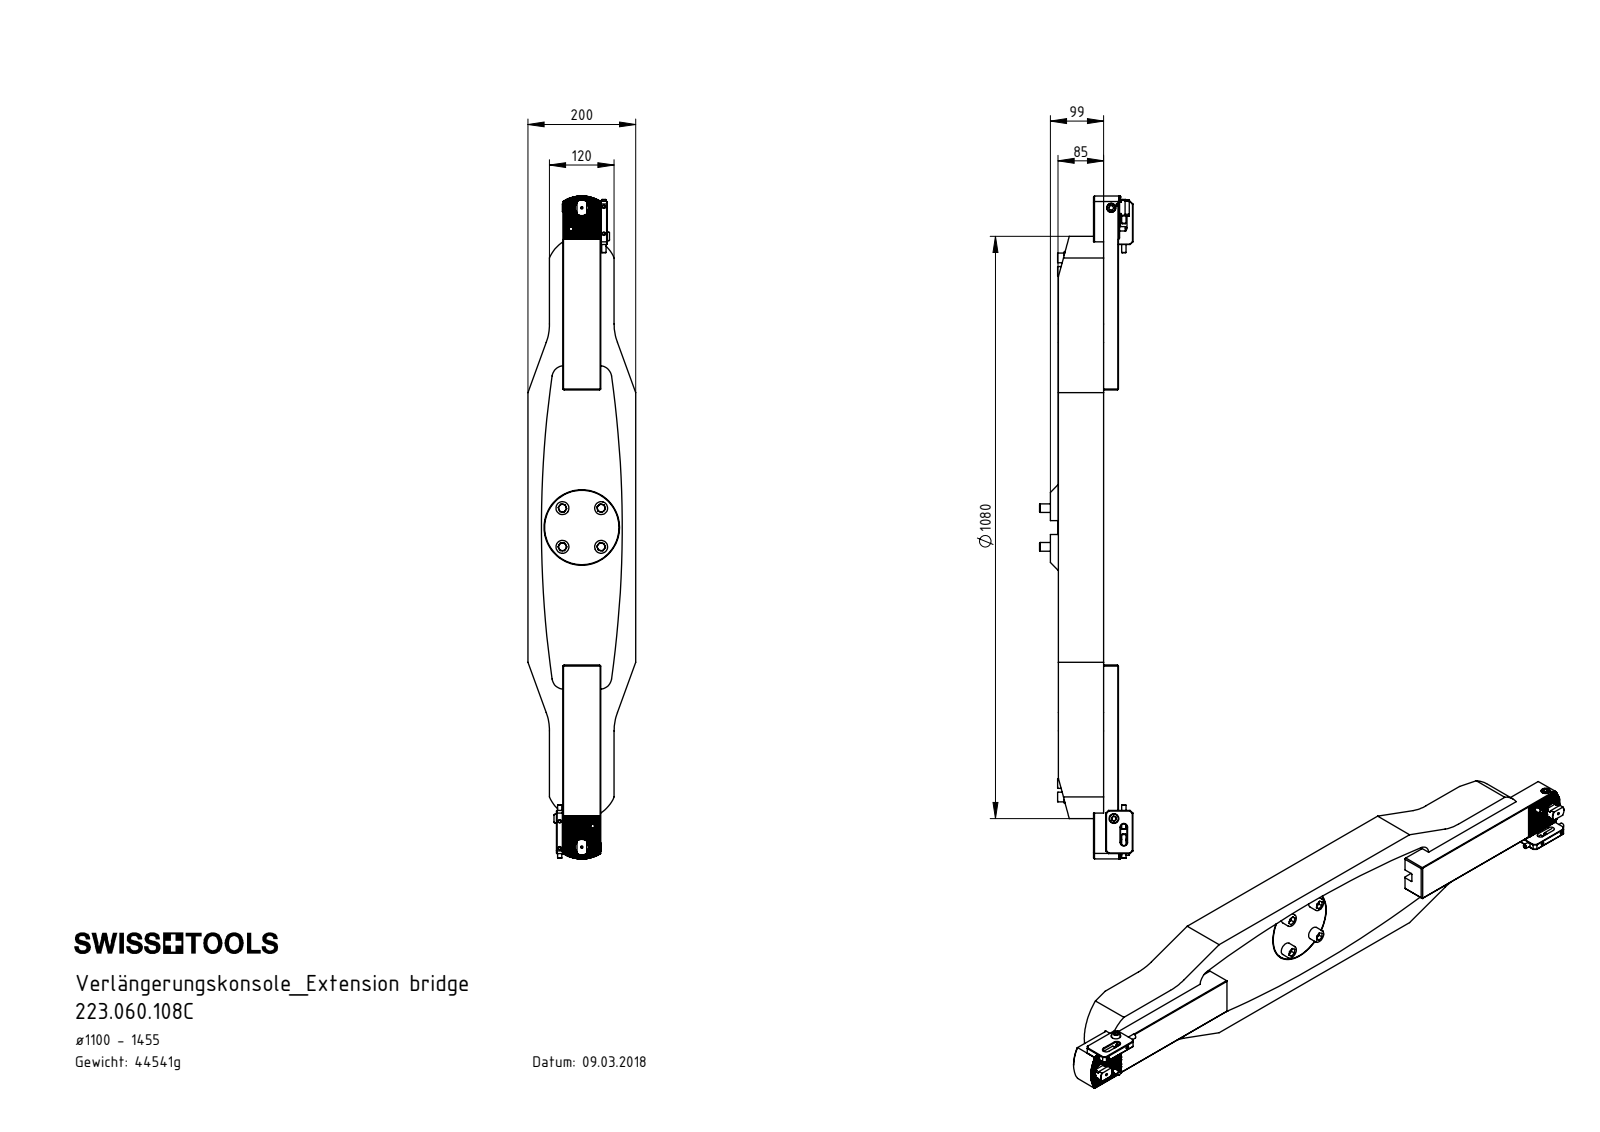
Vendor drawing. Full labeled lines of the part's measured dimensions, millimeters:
Part name (STEP PRODUCT): 223.060.108C; DIN 179 - D12xD18x12; ISO 4762 - M16 x 80; VK3-ER1.001.005_A (+8 more)
STEP written by: SolidWorks 2017 (CONFIG_CONTROL_DESIGN)
Units: millimetres
Bodies: 46 solids, 2145 faces (916 planar, 736 cylindrical, 493 other)
Overall size (bounding box): 1230 × 200 × 173
Volume: 11 790 000 mm³ · Surface area: 1 129 000 mm²
Round holes (diameter × count): ⌀18 ×42, ⌀10.2 ×40, ⌀13 ×16, ⌀5 ×4, ⌀6 ×4, ⌀6.8 ×4, ⌀12 ×4, ⌀17 ×4, ⌀2 ×2, ⌀8 ×2, ⌀8.5 ×2, ⌀10.5 ×2
Round bosses / shafts (diameter × count): ⌀24 ×12, ⌀16 ×8, ⌀12 ×4, ⌀10 ×2, ⌀8 ×2, ⌀138 ×1
Partial cylindrical surfaces — rounded edges, fillets, slot ends (radius × count): R0.14 ×33, R2 ×22, R22 ×12, R15 ×6, R1.5 ×4, R5.5 ×4, R6 ×4, R8 ×4
Main face-to-face distances: 65, 40, 32, 135, 13, 45, 25, 44, 71, 20
Hole centre spacings: 25, 47.17, 50, 64.03, 40, 75, 85, 925
